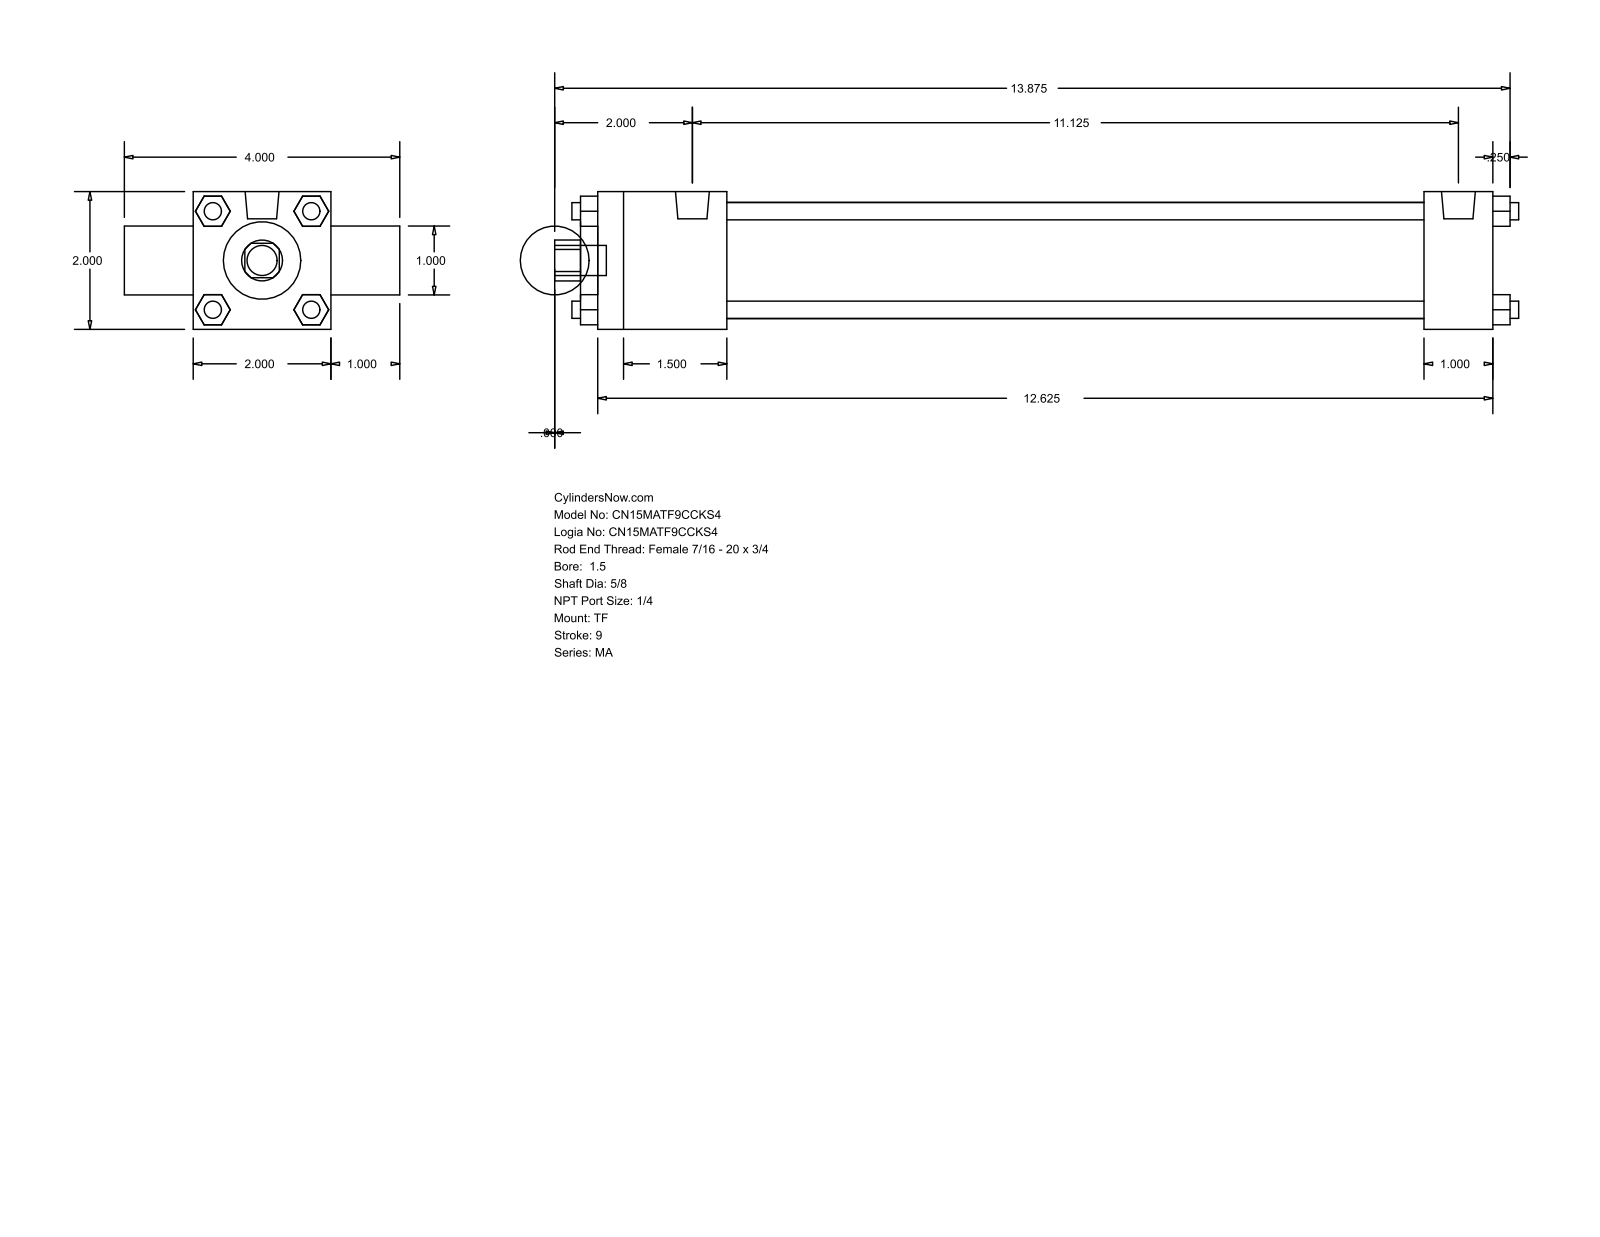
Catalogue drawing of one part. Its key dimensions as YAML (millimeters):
part_name: "MA_TF__0150_0.625"
step_written_by: "GSSL Pune (CONFIG_CONTROL_DESIGN)"
units: millimeters
bodies: {solids: 0, faces: 120, planar: 92, cylindrical: 28, other: 0}
overall_size: [355.6, 101.6, 50.8]
round_holes:
  - {diameter: 15.88, count: 1}
  - {diameter: 25.4, count: 1}
  - {diameter: 28.57, count: 1}
  - {diameter: 42.93, count: 1}
round_bosses_or_shafts:
  - {diameter: 6.35, count: 4}
  - {diameter: 7.94, count: 3}
  - {diameter: 12.49, count: 2}
  - {diameter: 11.11, count: 1}
partial_cylinders:
  - {radius: 7.54, count: 1}
face_to_face_distances: [50.8, 330.19, 25.4, 76.2, 47.62, 304.8, 257.18, 282.57, 25.39, 6.35]
